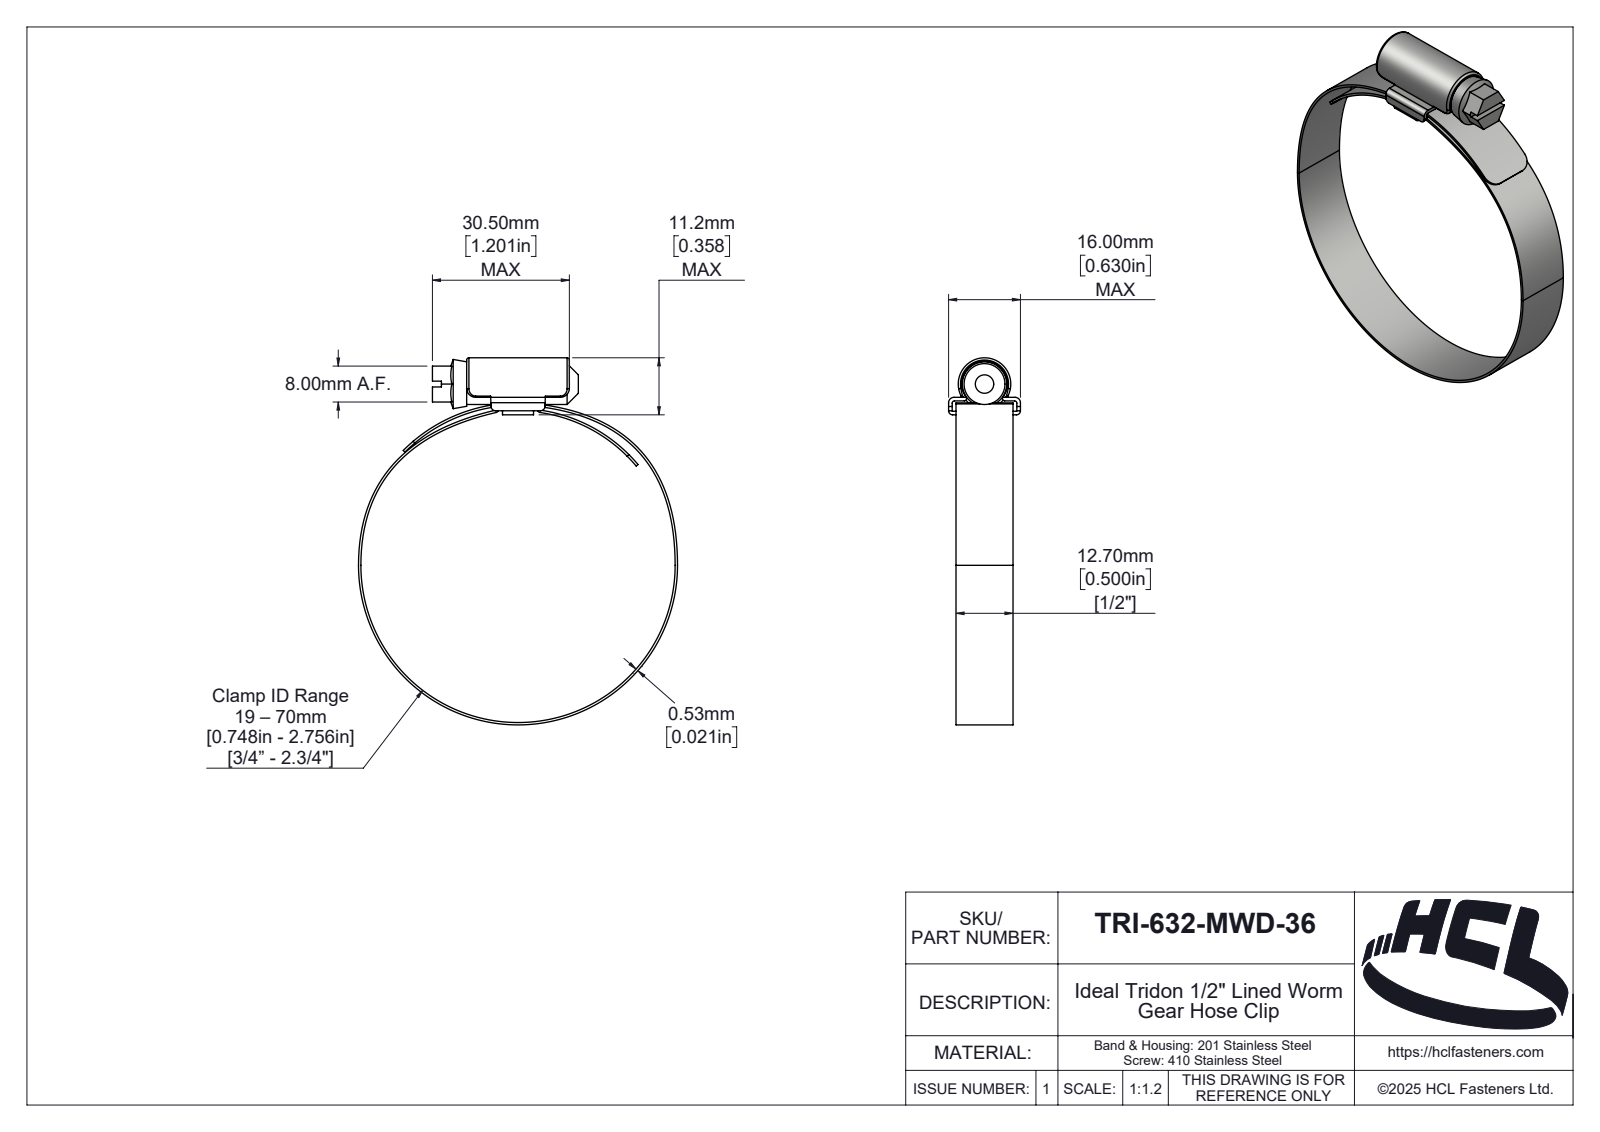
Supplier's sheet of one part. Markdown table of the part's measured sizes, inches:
| quantity | value |
| --- | --- |
| part name | TRI-632-MWD-36 |
| STEP written by | SolidWorks 2025 (AUTOMOTIVE_DESIGN) |
| units | inches |
| bodies | 3 solids, 217 faces (49 planar, 99 cylindrical, 69 other) |
| overall size | 3.218 × 2.798 × 0.63 |
| volume | 0.278 in³ |
| surface area | 15.79 in² |
| round bosses / shafts (diameter × count) | 0.358 × 1 |
| partial cylindrical surfaces (radius × count) | 0.02 × 10, 0.118 × 4, 0.004 × 2, 0.035 × 2, 0.039 × 2, 0.041 × 2, 0.047 × 2, 0.079 × 2 |
| main face-to-face distances | 0.031, 0.5, 0.122, 0.091, 0.154, 0.065, 0.565, 0.598, 0.033, 0.533 |
